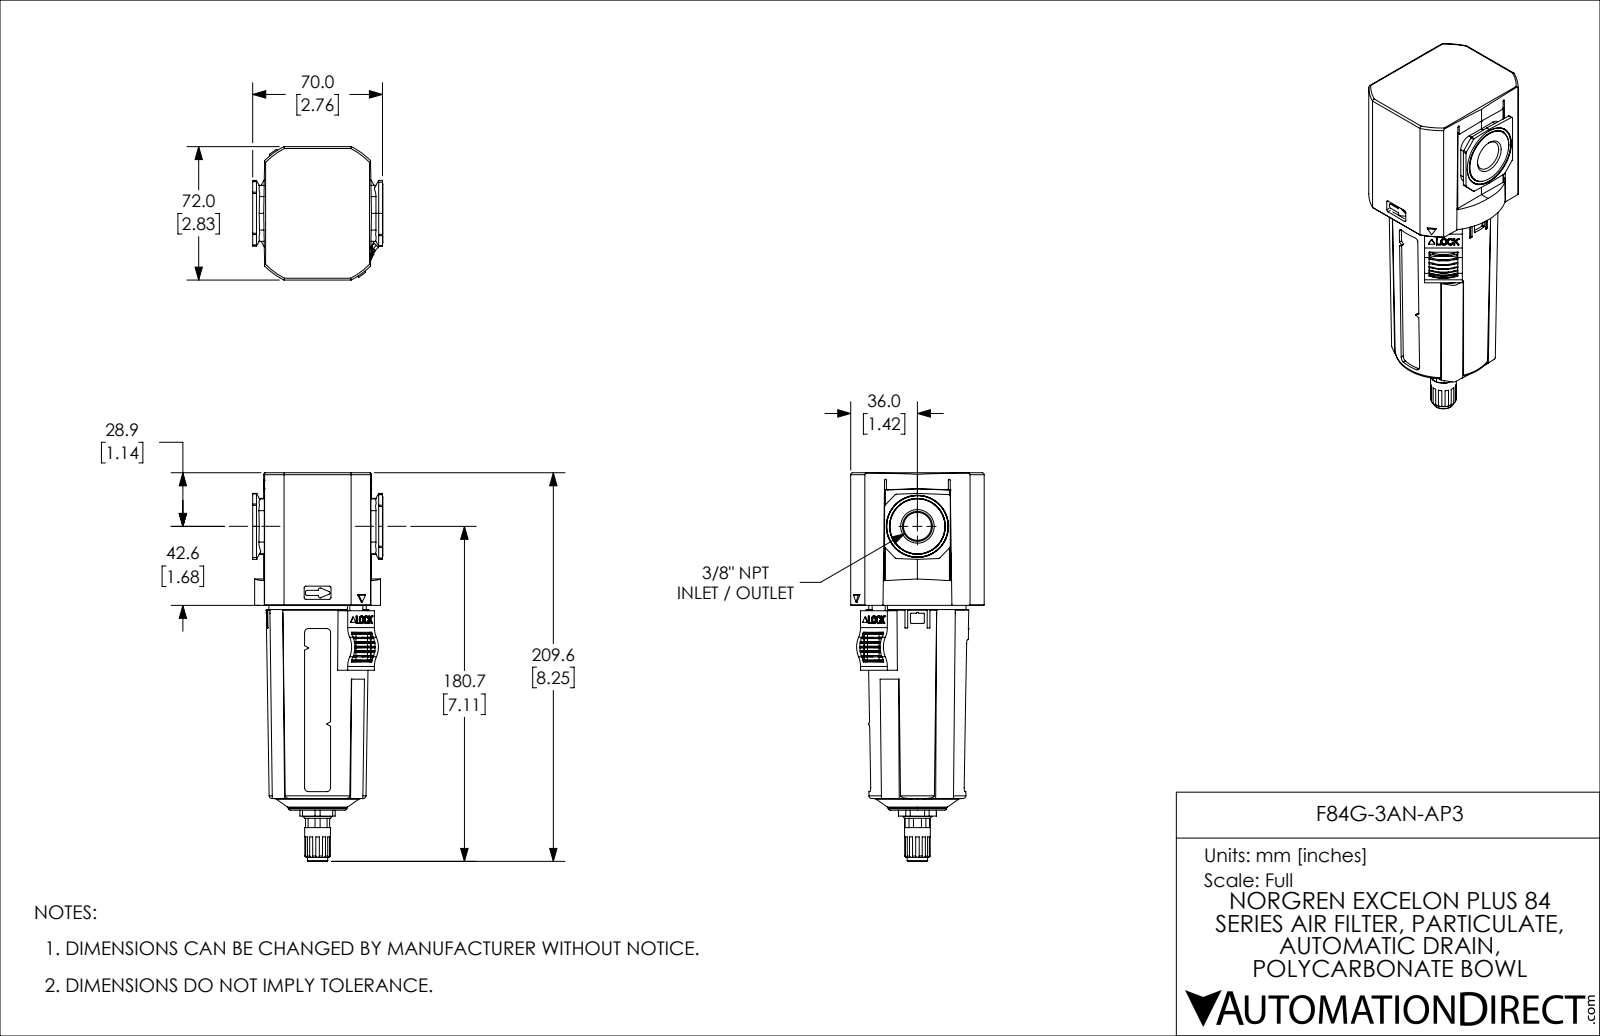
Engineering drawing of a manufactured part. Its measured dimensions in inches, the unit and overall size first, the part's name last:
Units: inches
Overall size (bounding box): 8.251 × 2.835 × 2.766
Round holes (diameter × count): ⌀0.163 ×2, ⌀0.22 ×1, ⌀0.246 ×1, ⌀0.776 ×1, ⌀0.969 ×1, ⌀2.461 ×1
Round bosses / shafts (diameter × count): ⌀0.315 ×2, ⌀0.276 ×2, ⌀1 ×1, ⌀0.969 ×1, ⌀0.907 ×1, ⌀0.617 ×1, ⌀0.547 ×1, ⌀0.433 ×1
Partial cylindrical surfaces — rounded edges, fillets, slot ends (radius × count): R0.039 ×44, R0.02 ×40, R0.01 ×24, R0.028 ×16, R0.008 ×10, R0.038 ×8, R0.045 ×8, R0.06 ×8
Main face-to-face distances: 0.059, 2.411, 2.352, 2.835, 0.035, 2.317, 2.376, 2.756, 0.404, 0.439
Hole centre spacings: 0.594, 1.189
Volume: 28.11 in³ · Surface area: 149.2 in²
Bodies: 5 solids, 1089 faces (504 planar, 405 cylindrical, 180 other)
Part name (STEP PRODUCT): F84G-3AN-AP3
STEP written by: SolidWorks 2021 (CONFIG_CONTROL_DESIGN)
